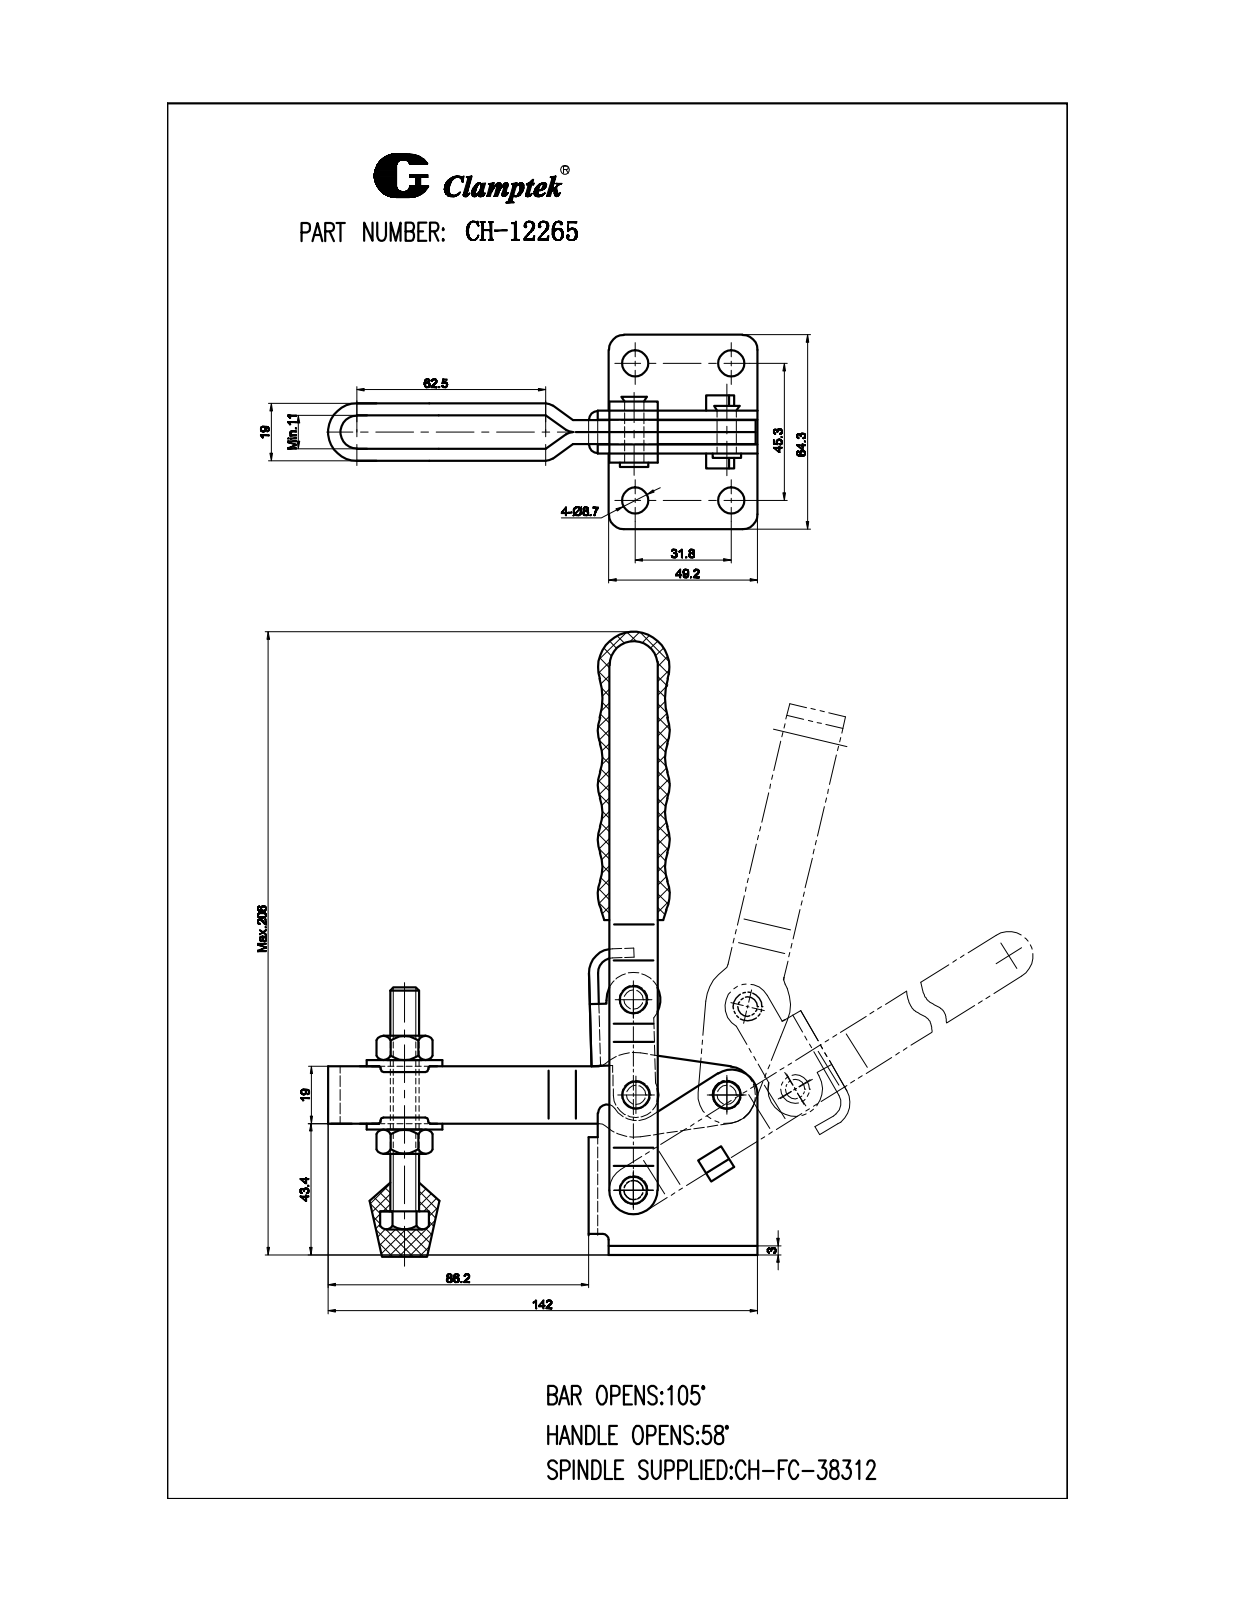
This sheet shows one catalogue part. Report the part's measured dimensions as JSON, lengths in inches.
{"part_name": "CH-12265-06; CH-12265-08; CH-12265-03 STRAIGHT HANDLE; CH-FC-38312 SPINDLE SUPPLIED (+8 more)", "step_written_by": "SolidWorks 2010 (CONFIG_CONTROL_DESIGN)", "units": "inches", "bodies": {"solids": 20, "faces": 887, "planar": 326, "cylindrical": 256, "other": 305}, "overall_size": [8.175, 5.548, 2.531], "volume_in3": 6.837, "surface_area_in2": 119.2, "round_holes": [[0.374, 5], [0.252, 4], [0.343, 4], [0.386, 2], [0.114, 1], [0.546, 1]], "round_bosses_or_shafts": [[0.378, 4], [0.354, 4], [0.374, 1], [0.098, 1]], "partial_cylinders_radius": [[0.118, 25], [0.079, 6], [0.197, 4], [0.315, 4], [0.157, 2], [0.157, 2], [0.335, 2], [0.492, 2]], "face_to_face_distances": [0.118, 0.157, 0.276, 0.433, 0.039, 0.394, 0.374, 0.315, 0.551, 0.059], "hole_center_spacings": [1.252, 1.783, 2.179, 4.256, 4.257, 1.181, 1.24, 1.241]}
